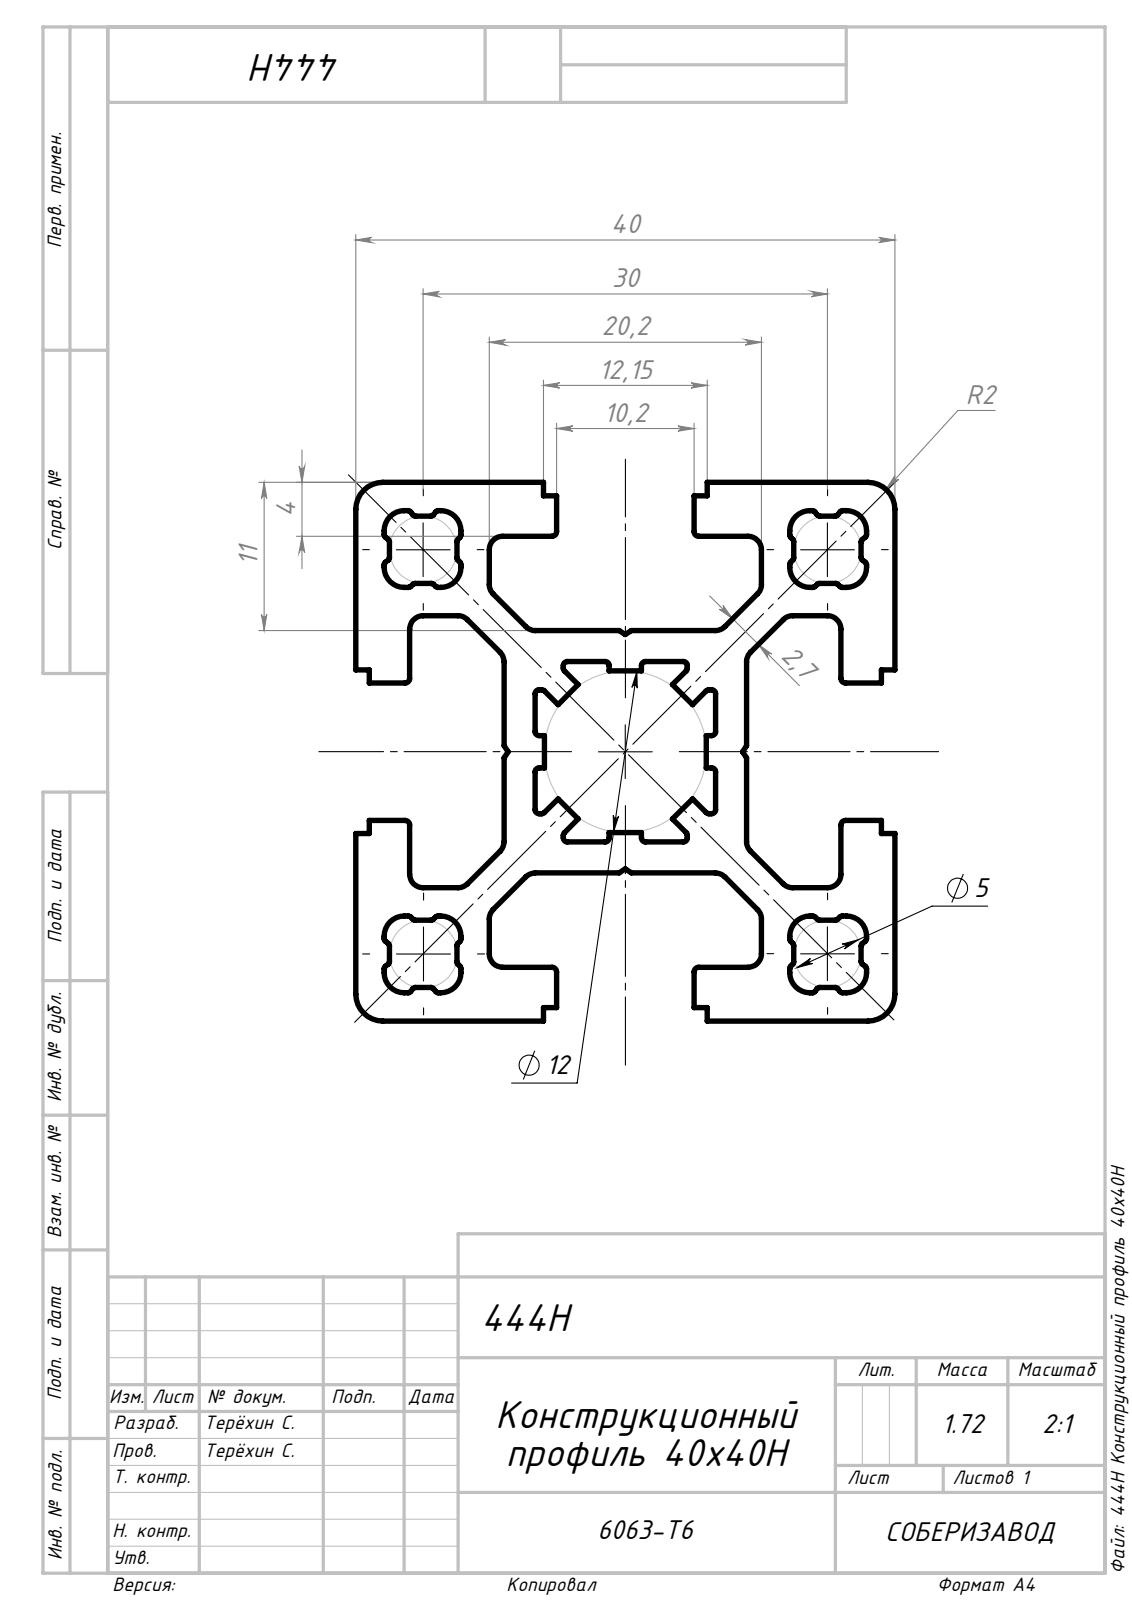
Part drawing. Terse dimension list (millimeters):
name: Сборка1
written by: SolidWorks 2021 (AUTOMOTIVE_DESIGN)
unit: mm
bodies: 1 solid, 334 faces (194 planar, 140 cylindrical, 0 other)
size: 1000 × 40 × 40
volume: 638 563 mm³; area: 458 306 mm²
rounds: 64× R0.25, 24× R0.3, 24× R1, 16× R1.5, 8× R0.35, 4× R2
face distances: 11, 29, 40, 25, 5, 4, 36, 7, 18, 13.3
